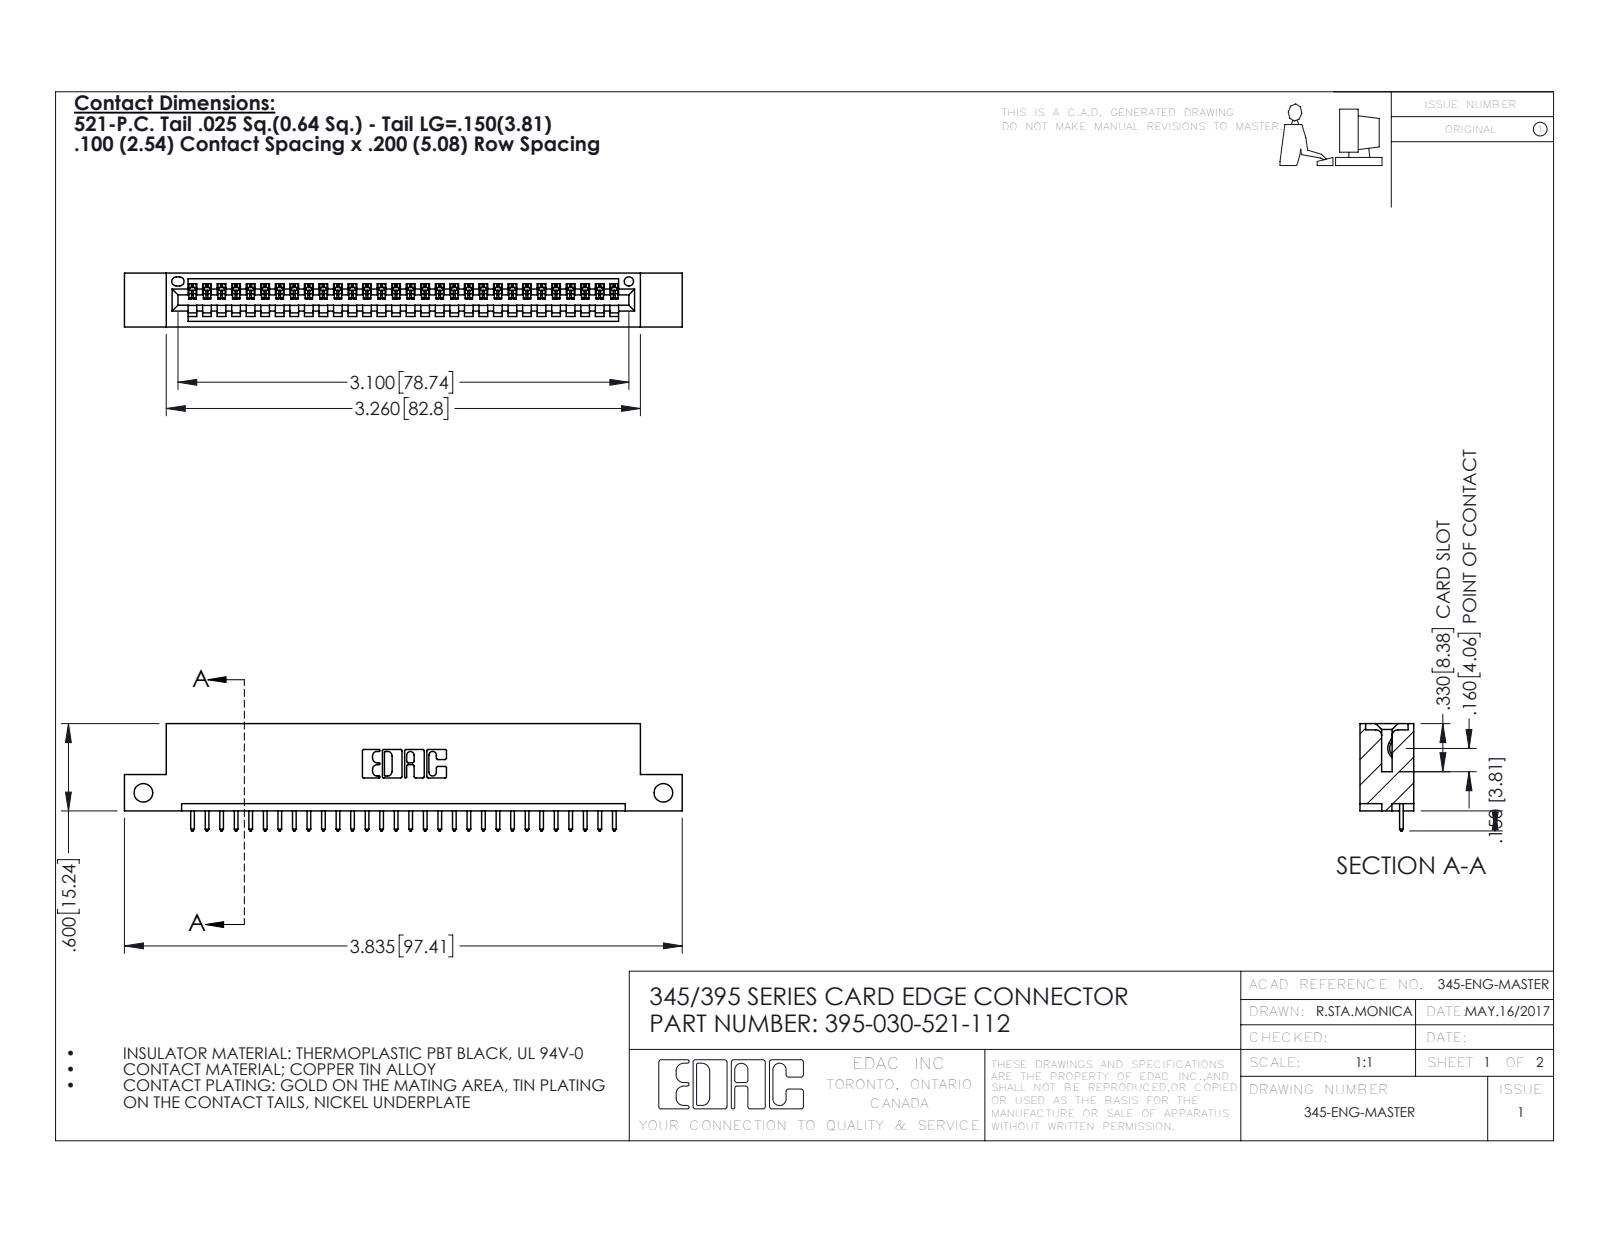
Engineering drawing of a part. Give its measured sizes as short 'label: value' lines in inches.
name: 345-292-001_345-293-121; 345 Part_Flush Mounting Lugs - Side Mount; 395-030-521-112
written by: SolidWorks 2016 (CONFIG_CONTROL_DESIGN)
unit: in
bodies: 31 solids, 1866 faces (1280 planar, 586 cylindrical, 0 other)
size: 3.835 × 0.737 × 0.37
volume: 0.548 in³; area: 17.51 in²
holes: 2× ⌀0.128, 1× ⌀0.064
rounds: 60× R0.006, 60× R0.01, 22× R0.01, 6× R0.007, 6× R0.031, 3× R0.026, 2× R0.031, 2× R0.04
face distances: 0.298, 0.072, 0.2, 0.37, 0.098, 0.272, 0.025, 0.225, 0.149, 0.072
hole spacings: 3.575
